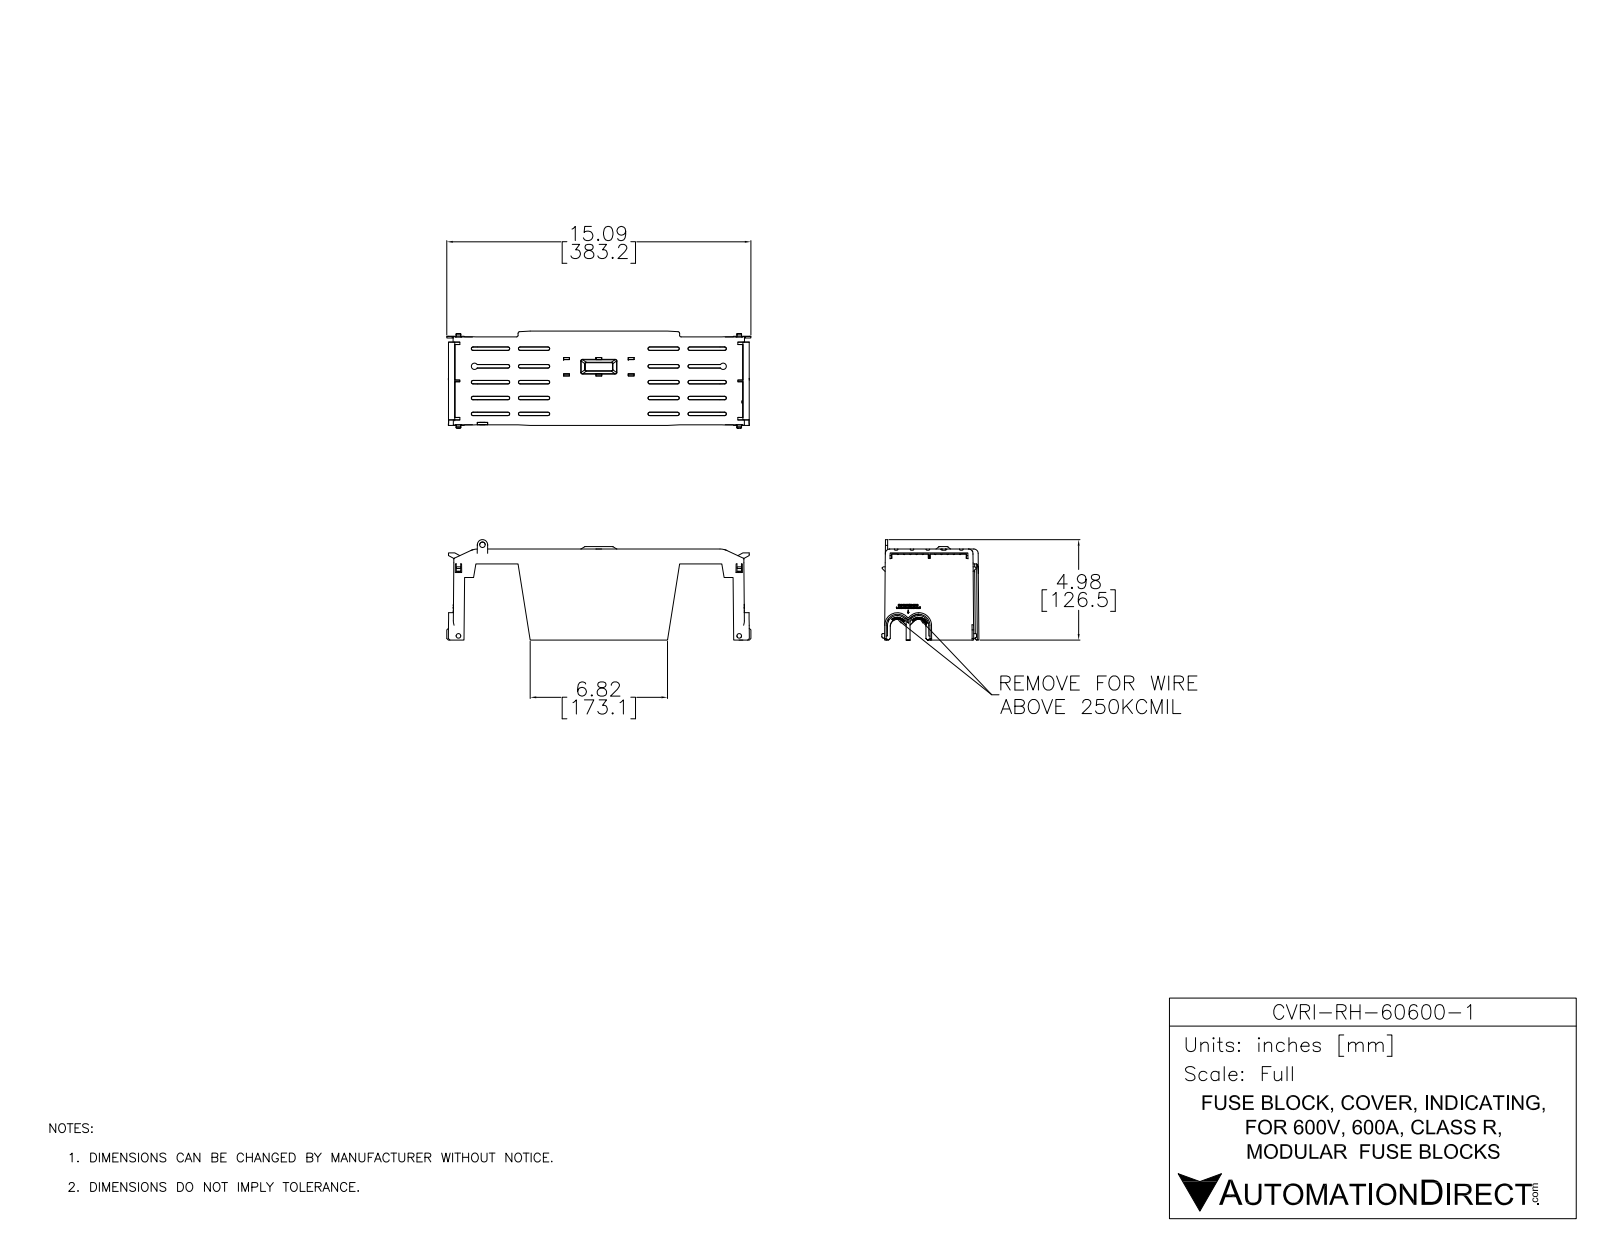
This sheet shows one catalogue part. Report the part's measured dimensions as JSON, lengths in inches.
{"part_name": "CVRI-RH-60600-1", "step_written_by": "SolidWorks 2017 (AUTOMOTIVE_DESIGN)", "units": "inches", "bodies": {"solids": 1, "faces": 2399, "planar": 1630, "cylindrical": 123, "other": 646}, "overall_size": [15.085, 4.983, 4.817], "volume_in3": 15.84, "surface_area_in2": 413.6, "round_holes": [[0.276, 1]], "round_bosses_or_shafts": [[0.228, 2]], "partial_cylinders_radius": [[0.039, 18], [0.118, 8], [0.138, 7], [0.217, 7], [0.079, 4], [0.354, 4], [0.492, 4], [0.551, 4]], "face_to_face_distances": [0.079, 0.256, 0.177, 0.795, 0.197, 0.335, 0.803, 0.118, 0.402, 1.598]}
